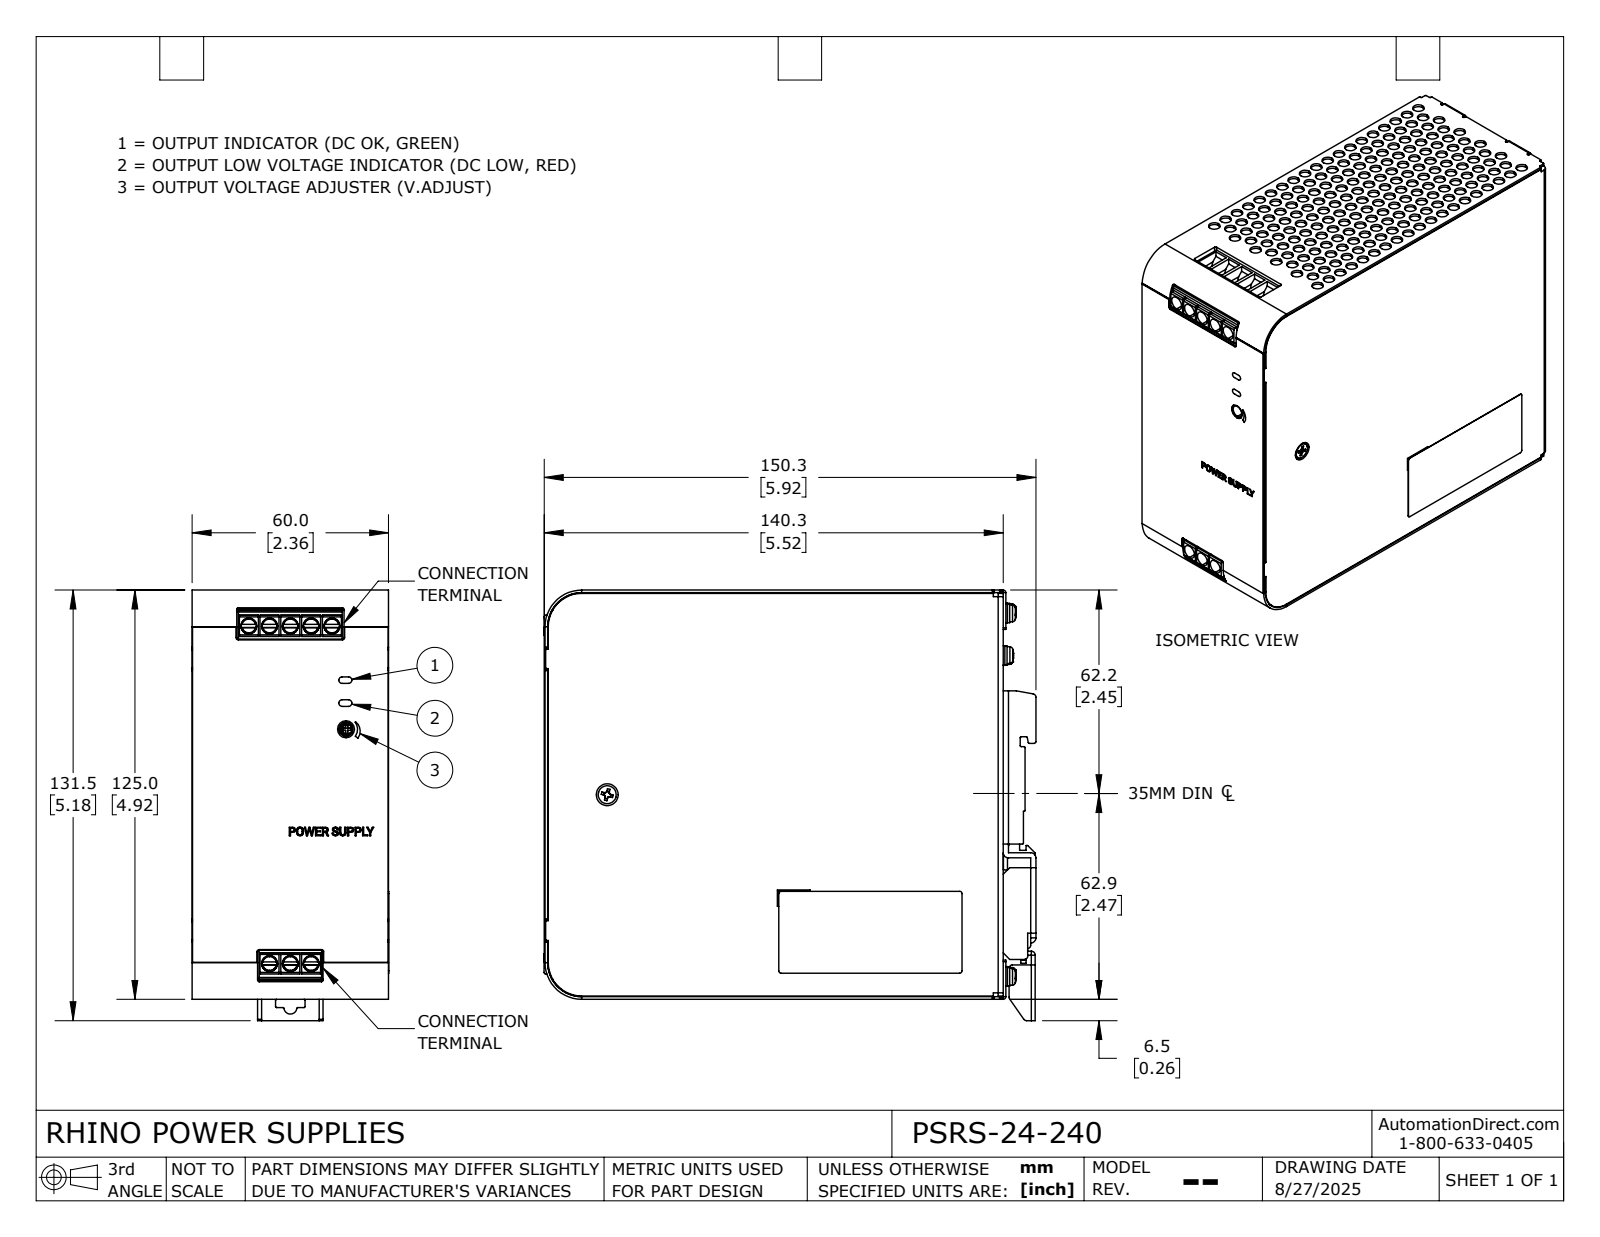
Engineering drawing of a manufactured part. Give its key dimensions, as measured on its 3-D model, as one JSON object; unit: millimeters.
{"part_name": "PSRS-24-240", "step_written_by": "SolidWorks 2024 (AUTOMOTIVE_DESIGN)", "units": "millimeters", "bodies": {"solids": 2, "faces": 3059, "planar": 1489, "cylindrical": 1291, "other": 279}, "overall_size": [150.3, 131.5, 60.05], "volume_mm3": 1048000, "surface_area_mm2": 95151, "round_holes": [[4, 210], [3.1, 10], [3.5, 10], [4.65, 8], [4.85, 8], [3.8, 6], [3.6, 5], [2.5, 4], [6.7, 4], [1.5, 1], [3.4, 1], [4.2, 1]], "round_bosses_or_shafts": [[3, 16], [6, 10], [5.9, 10], [4.75, 8], [5.5, 4]], "partial_cylinders_radius": [[0.3, 61], [0.5, 37], [0.15, 14], [1, 14], [1.6, 13], [1.2, 9], [0.1, 7], [0.6, 2]], "face_to_face_distances": [60, 0.8, 124.2, 140.25, 125, 1.6, 123.4, 8.4, 13.6, 1.2], "hole_center_spacings": [11.64, 5.6, 15.15, 11.2, 21.15, 19.65, 10.2, 23.27]}
